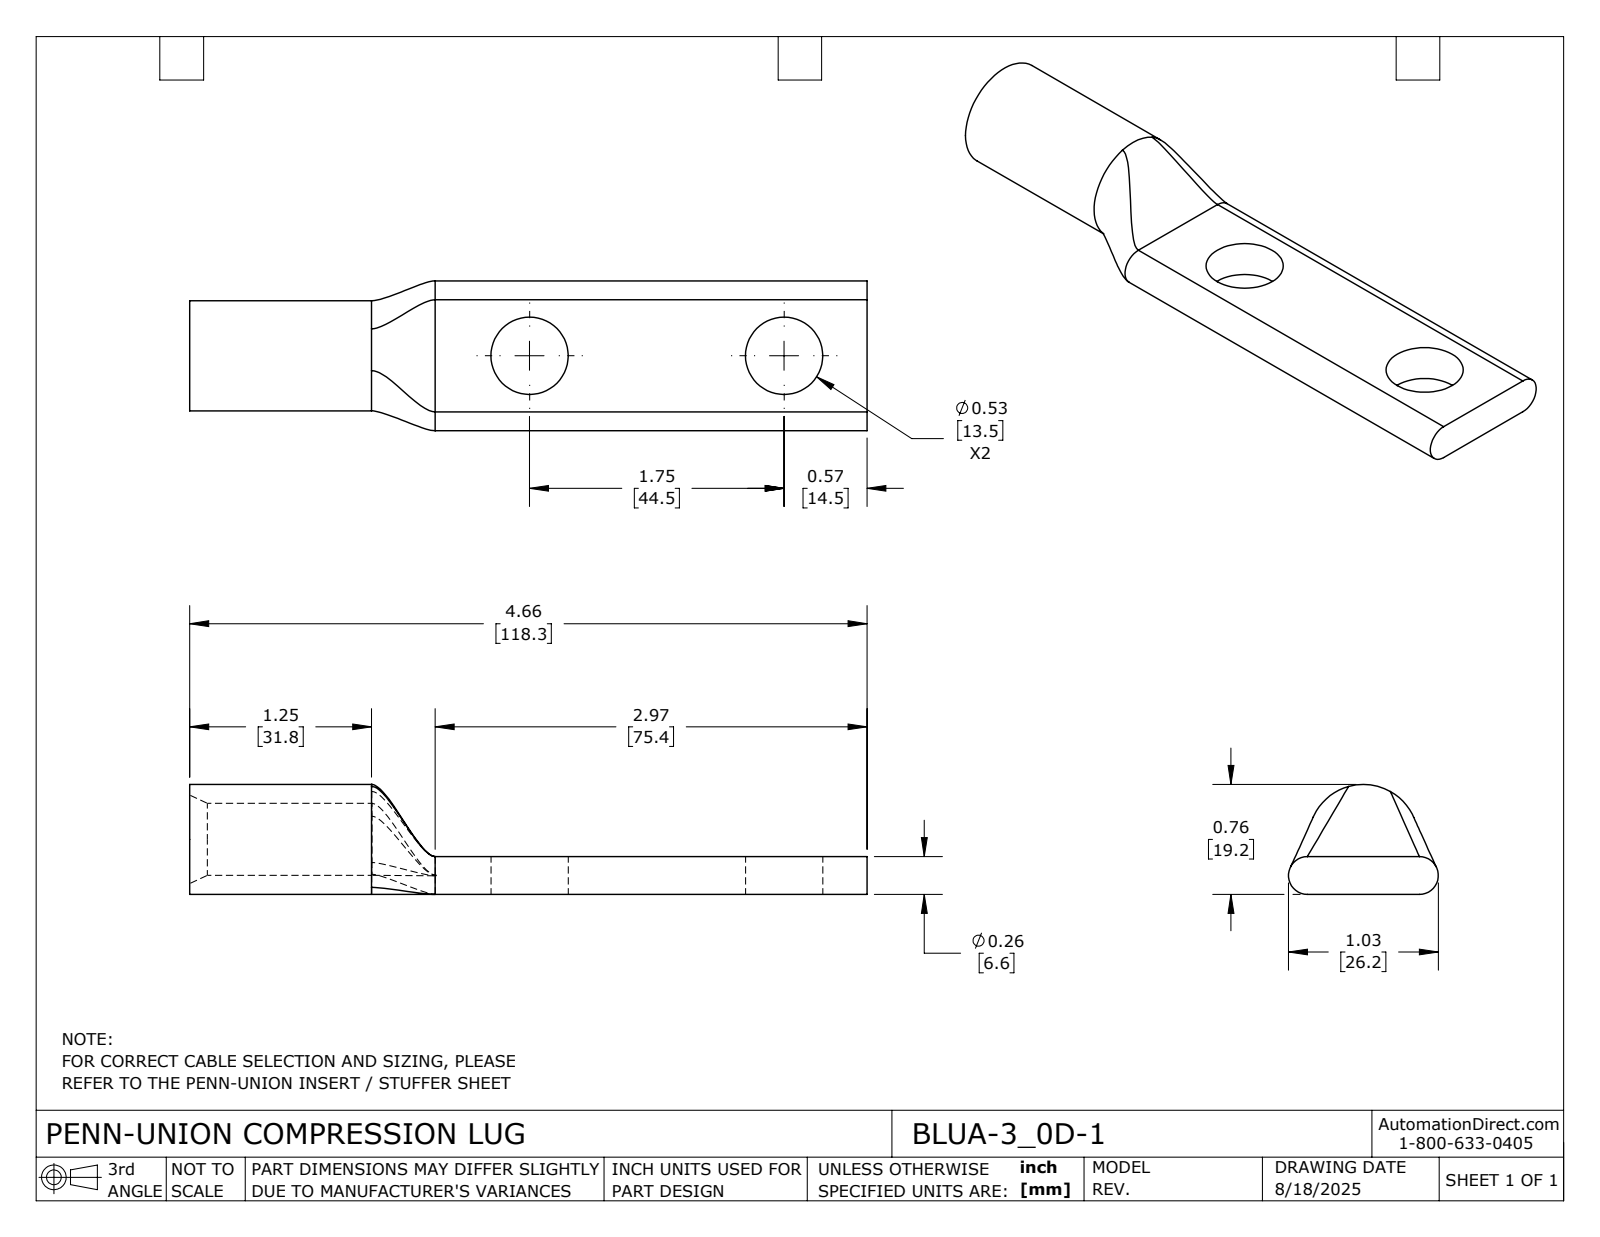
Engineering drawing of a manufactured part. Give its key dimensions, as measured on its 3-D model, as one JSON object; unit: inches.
{"part_name": "BLUA-3_0D-1", "step_written_by": "SolidWorks 2024 (CONFIG_CONTROL_DESIGN)", "units": "inches", "bodies": {"solids": 1, "faces": 26, "planar": 5, "cylindrical": 11, "other": 10}, "overall_size": [4.656, 1.03, 0.756], "volume_in3": 1.062, "surface_area_in2": 14.34, "round_holes": [[0.531, 2], [0.495, 1]], "round_bosses_or_shafts": [[0.756, 1]], "partial_cylinders_radius": [[0.13, 2]], "face_to_face_distances": [0.26, 4.656, 1.687, 2.969], "hole_center_spacings": [1.75]}
